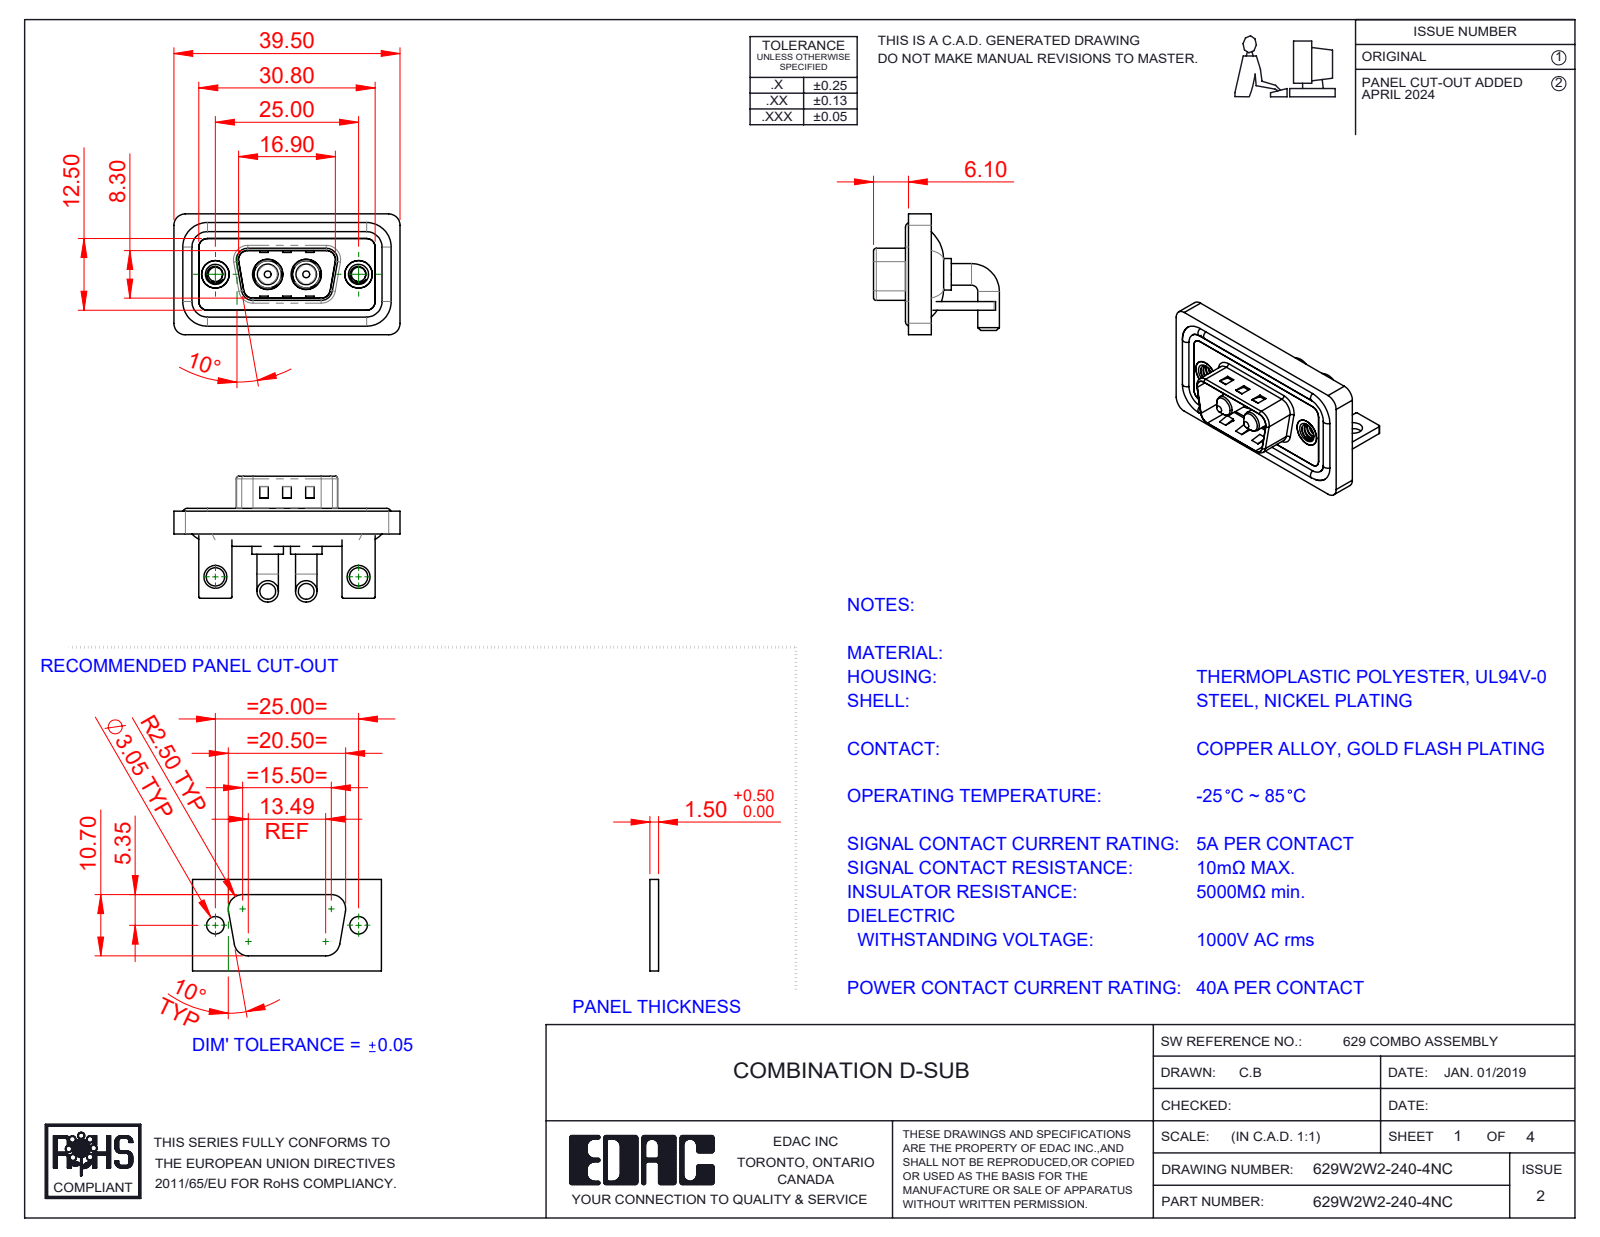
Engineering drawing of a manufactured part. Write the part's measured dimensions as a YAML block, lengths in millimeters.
part_name: "629Combo Shell Front_09 Contacts; 629Combo Threaded Rivet_B; 629Combo Waterproof Housing_09 Contacts; 629Combo Shell Rear_09 Contacts (+4 more)"
step_written_by: "SolidWorks 2023 (CONFIG_CONTROL_DESIGN)"
units: millimeters
bodies: {solids: 13, faces: 535, planar: 185, cylindrical: 240, other: 110}
overall_size: [39.5, 21.98, 21.1]
volume: 5002
surface_area: 7843
round_holes:
  - {diameter: 2.5, count: 2}
  - {diameter: 3.2, count: 2}
  - {diameter: 4, count: 2}
  - {diameter: 4.8, count: 2}
  - {diameter: 4.85, count: 2}
  - {diameter: 5, count: 2}
  - {diameter: 5.3, count: 2}
round_bosses_or_shafts:
  - {diameter: 3.75, count: 4}
  - {diameter: 1.6, count: 4}
  - {diameter: 5.5, count: 2}
  - {diameter: 5.2, count: 2}
  - {diameter: 4.9, count: 2}
  - {diameter: 4.75, count: 2}
  - {diameter: 3.6, count: 2}
partial_cylinders:
  - {radius: 2, count: 19}
  - {radius: 1.5, count: 18}
  - {radius: 0.25, count: 16}
  - {radius: 0.5, count: 9}
  - {radius: 1.6, count: 8}
  - {radius: 0.6, count: 4}
  - {radius: 0.65, count: 4}
  - {radius: 0.9, count: 4}
face_to_face_distances: [0.4, 1.5, 2.9, 0.8, 1.1, 1.2, 2.1, 1.6, 3.7, 2.5]
hole_center_spacings: [9.14, 15.86, 25, 6.72]
